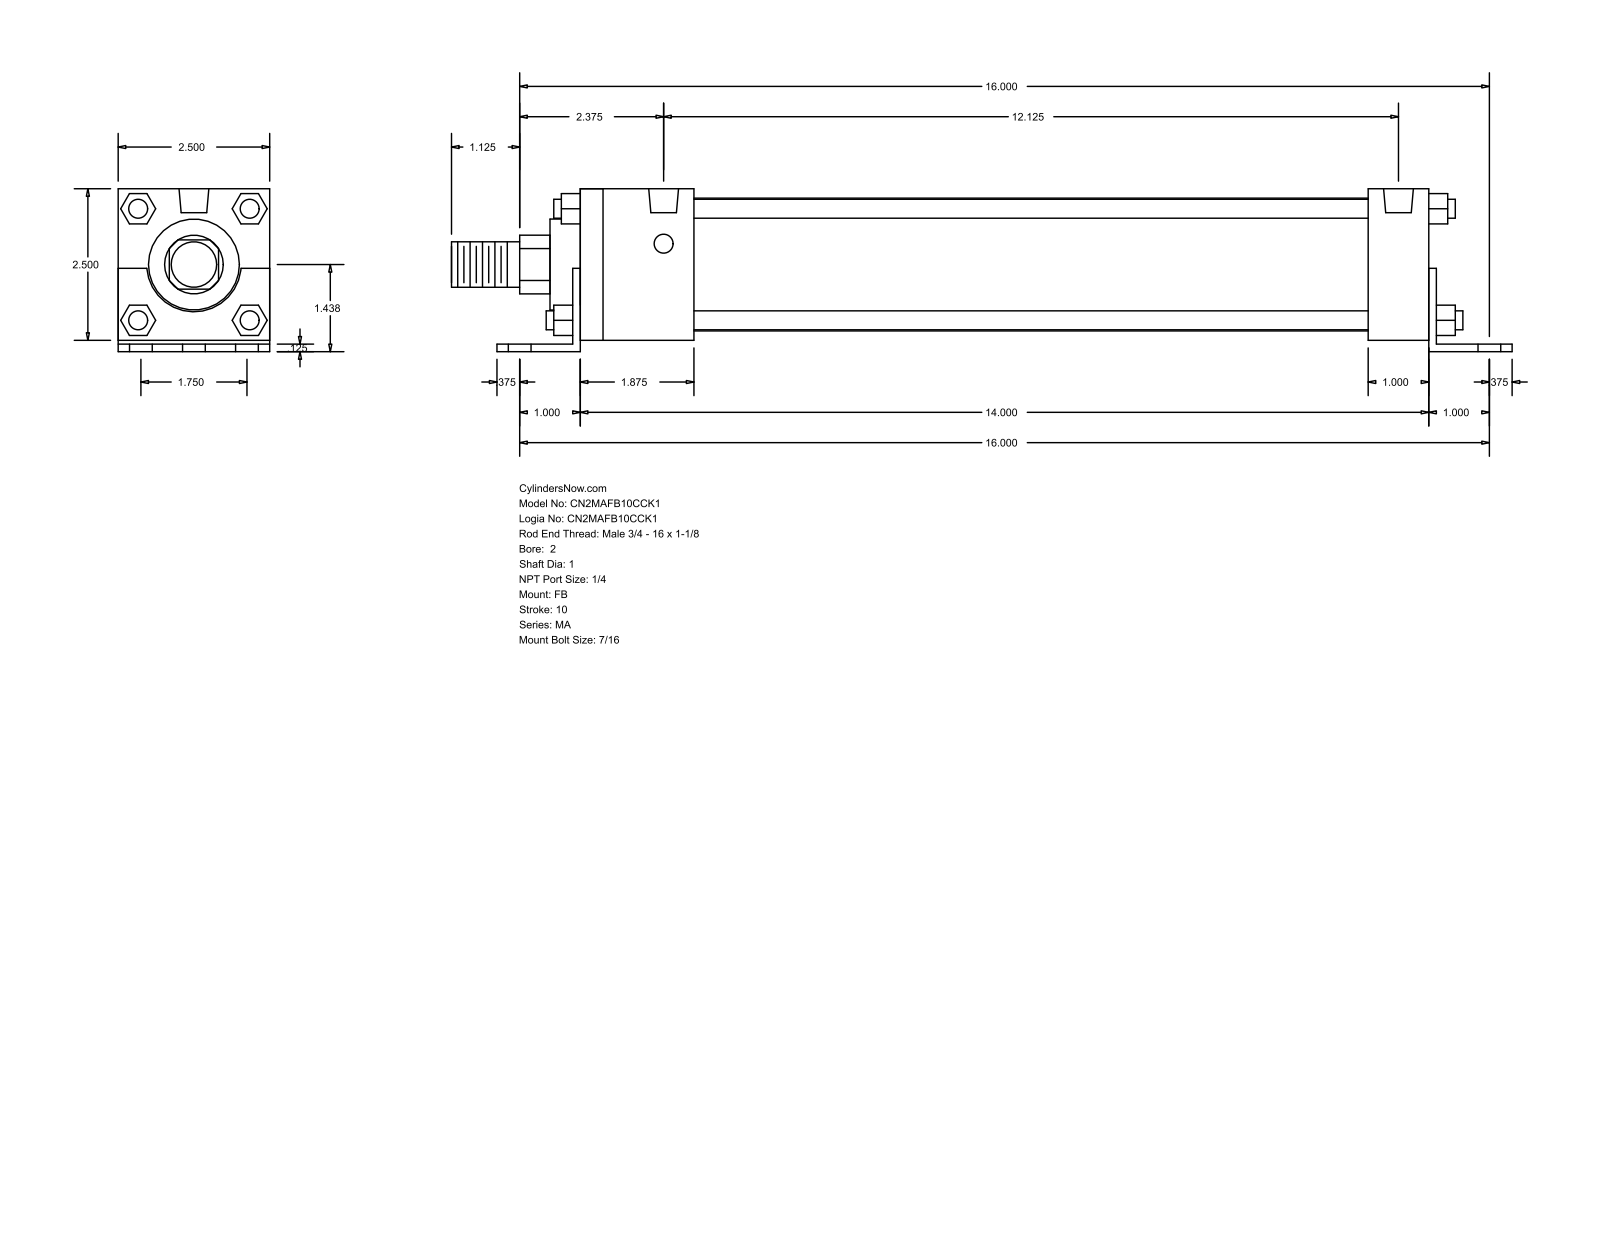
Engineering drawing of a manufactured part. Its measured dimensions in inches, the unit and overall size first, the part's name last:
Units: inches
Overall size (bounding box): 17.5 × 2.687 × 2.5
Round holes (diameter × count): ⌀0.437 ×6, ⌀0.313 ×4, ⌀0.492 ×2
Round bosses / shafts (diameter × count): ⌀0.313 ×4, ⌀2.19 ×1, ⌀1.5 ×1, ⌀1 ×1, ⌀0.75 ×1
Partial cylindrical surfaces — rounded edges, fillets, slot ends (radius × count): R0.484 ×1, R0.78 ×1
Main face-to-face distances: 2.5, 0.125, 0.187, 2.687, 0.063, 2.563, 0.5, 0.125, 14, 14.125
Hole centre spacings: 0.875, 16.024, 16, 1.737, 1.75, 2.531, 12.125, 13.653
Bodies: 0 solids, 140 faces (105 planar, 35 cylindrical, 0 other)
Part name (STEP PRODUCT): MA_FB__0200_1
STEP written by: GSSL Pune (CONFIG_CONTROL_DESIGN)
